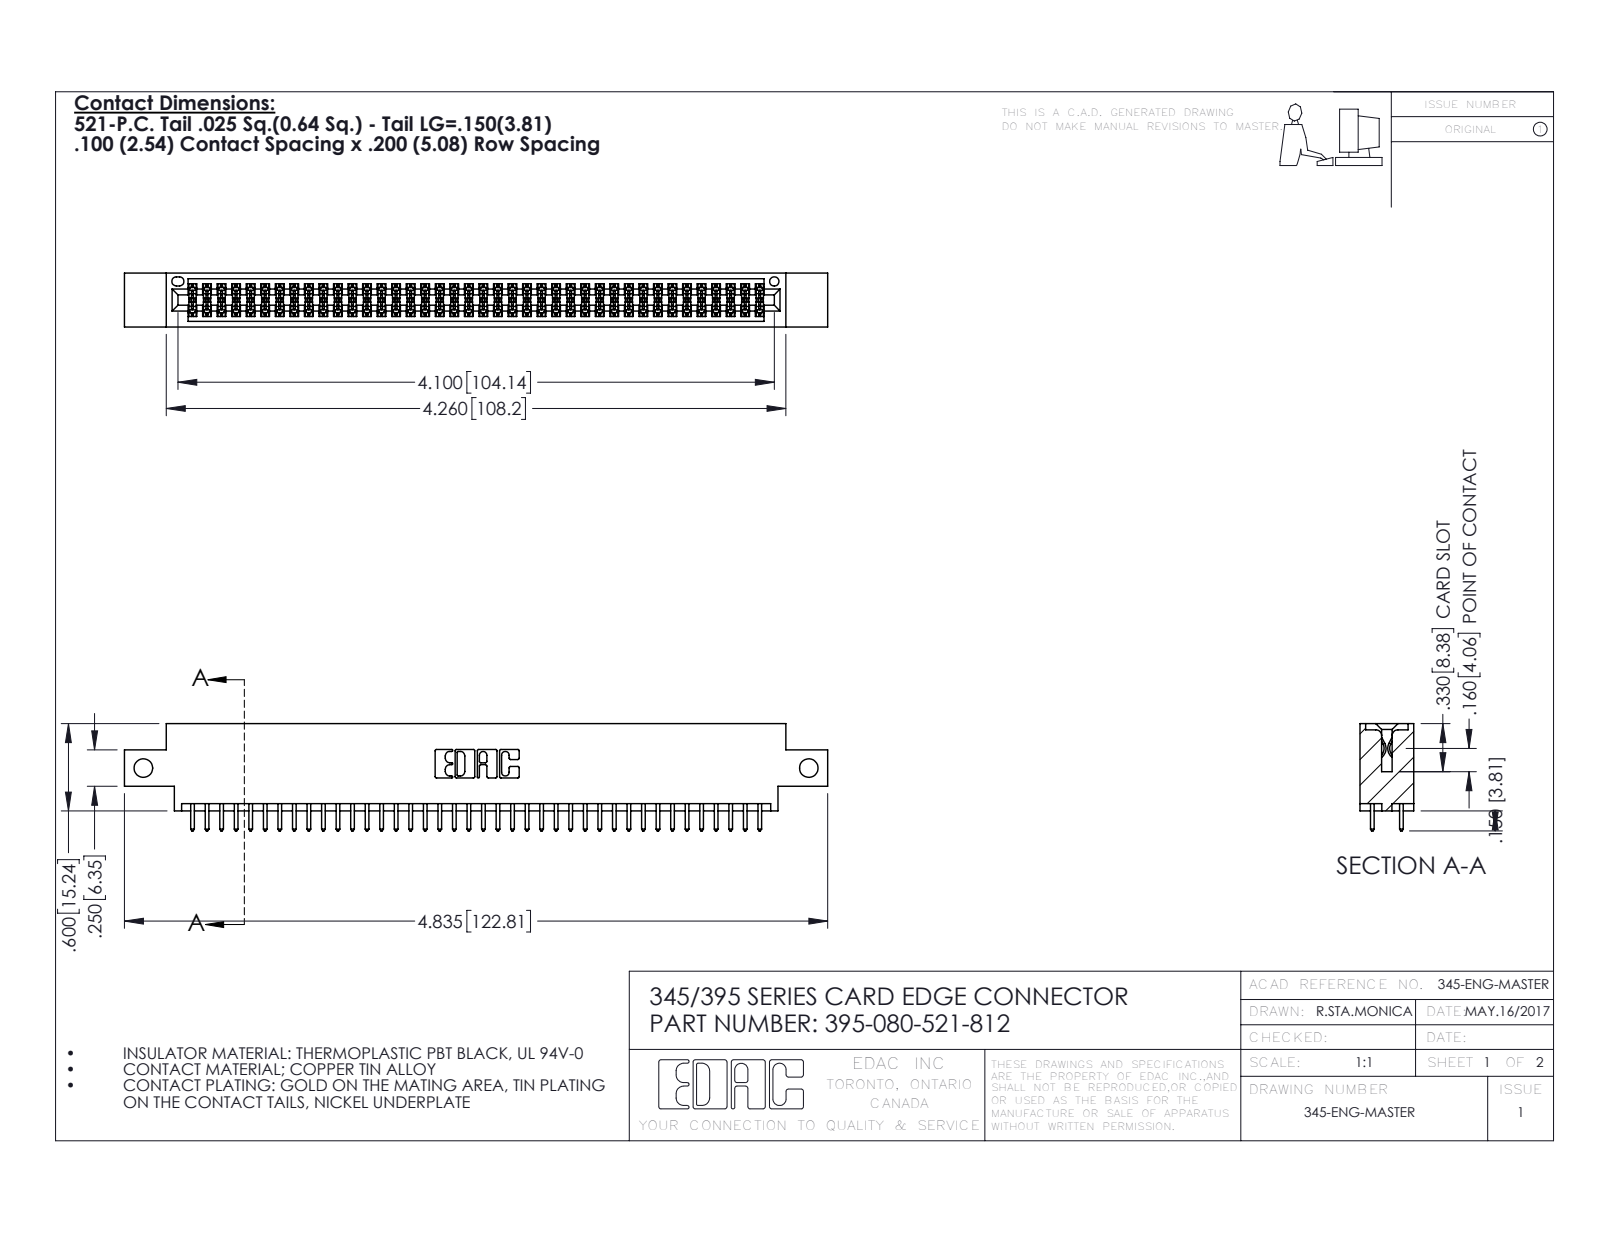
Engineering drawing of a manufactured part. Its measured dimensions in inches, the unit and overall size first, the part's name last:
Units: inches
Overall size (bounding box): 4.835 × 0.737 × 0.37
Round holes (diameter × count): ⌀0.128 ×2, ⌀0.064 ×1
Partial cylindrical surfaces — rounded edges, fillets, slot ends (radius × count): R0.006 ×120, R0.01 ×80, R0.01 ×22, R0.007 ×6, R0.031 ×6, R0.026 ×3, R0.014 ×2, R0.019 ×2
Main face-to-face distances: 0.072, 0.298, 0.2, 0.37, 0.098, 0.272, 0.025, 0.225, 0.175, 0.149
Hole centre spacings: 4.575
Volume: 0.713 in³ · Surface area: 26.38 in²
Bodies: 81 solids, 4130 faces (2724 planar, 1406 cylindrical, 0 other)
Part name (STEP PRODUCT): 395-080-521-812; 345 Part_0.170 Offset - Side Mount; 345-292-001_345-293-121
STEP written by: SolidWorks 2016 (CONFIG_CONTROL_DESIGN)
